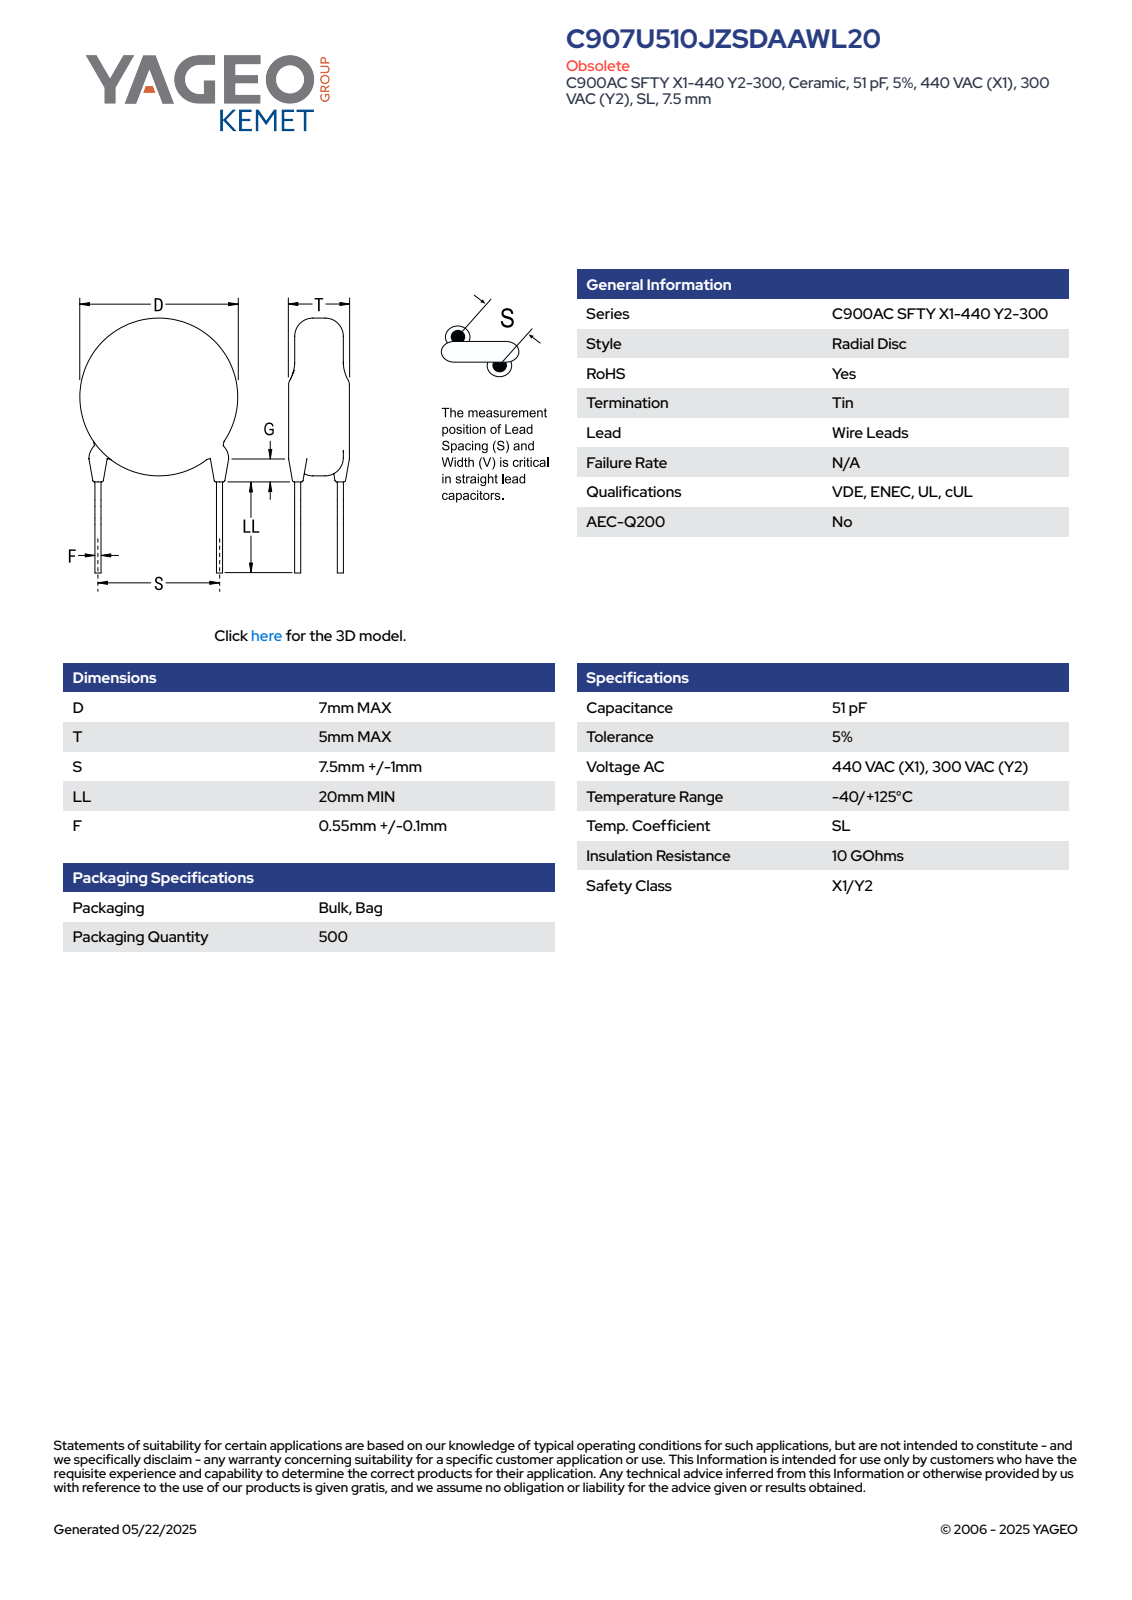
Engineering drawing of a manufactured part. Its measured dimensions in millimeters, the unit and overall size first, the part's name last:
Units: millimetres
Overall size (bounding box): 27.35 × 7.72 × 5
Round bosses / shafts (diameter × count): ⌀0.65 ×2, ⌀7 ×1
Main face-to-face distances: 5, 0.81, 24.25, 23.44, 3.3, 1.67, 3.52, 2.4, 2.49, 1.32
Volume: 200 mm³ · Surface area: 262 mm²
Bodies: 4 solids, 83 faces (61 planar, 6 cylindrical, 16 other)
Part name (STEP PRODUCT): CCD_STC900_D7T5S7.5LL20F0.65G3
STEP written by: SolidWorks 2014 (AUTOMOTIVE_DESIGN)
